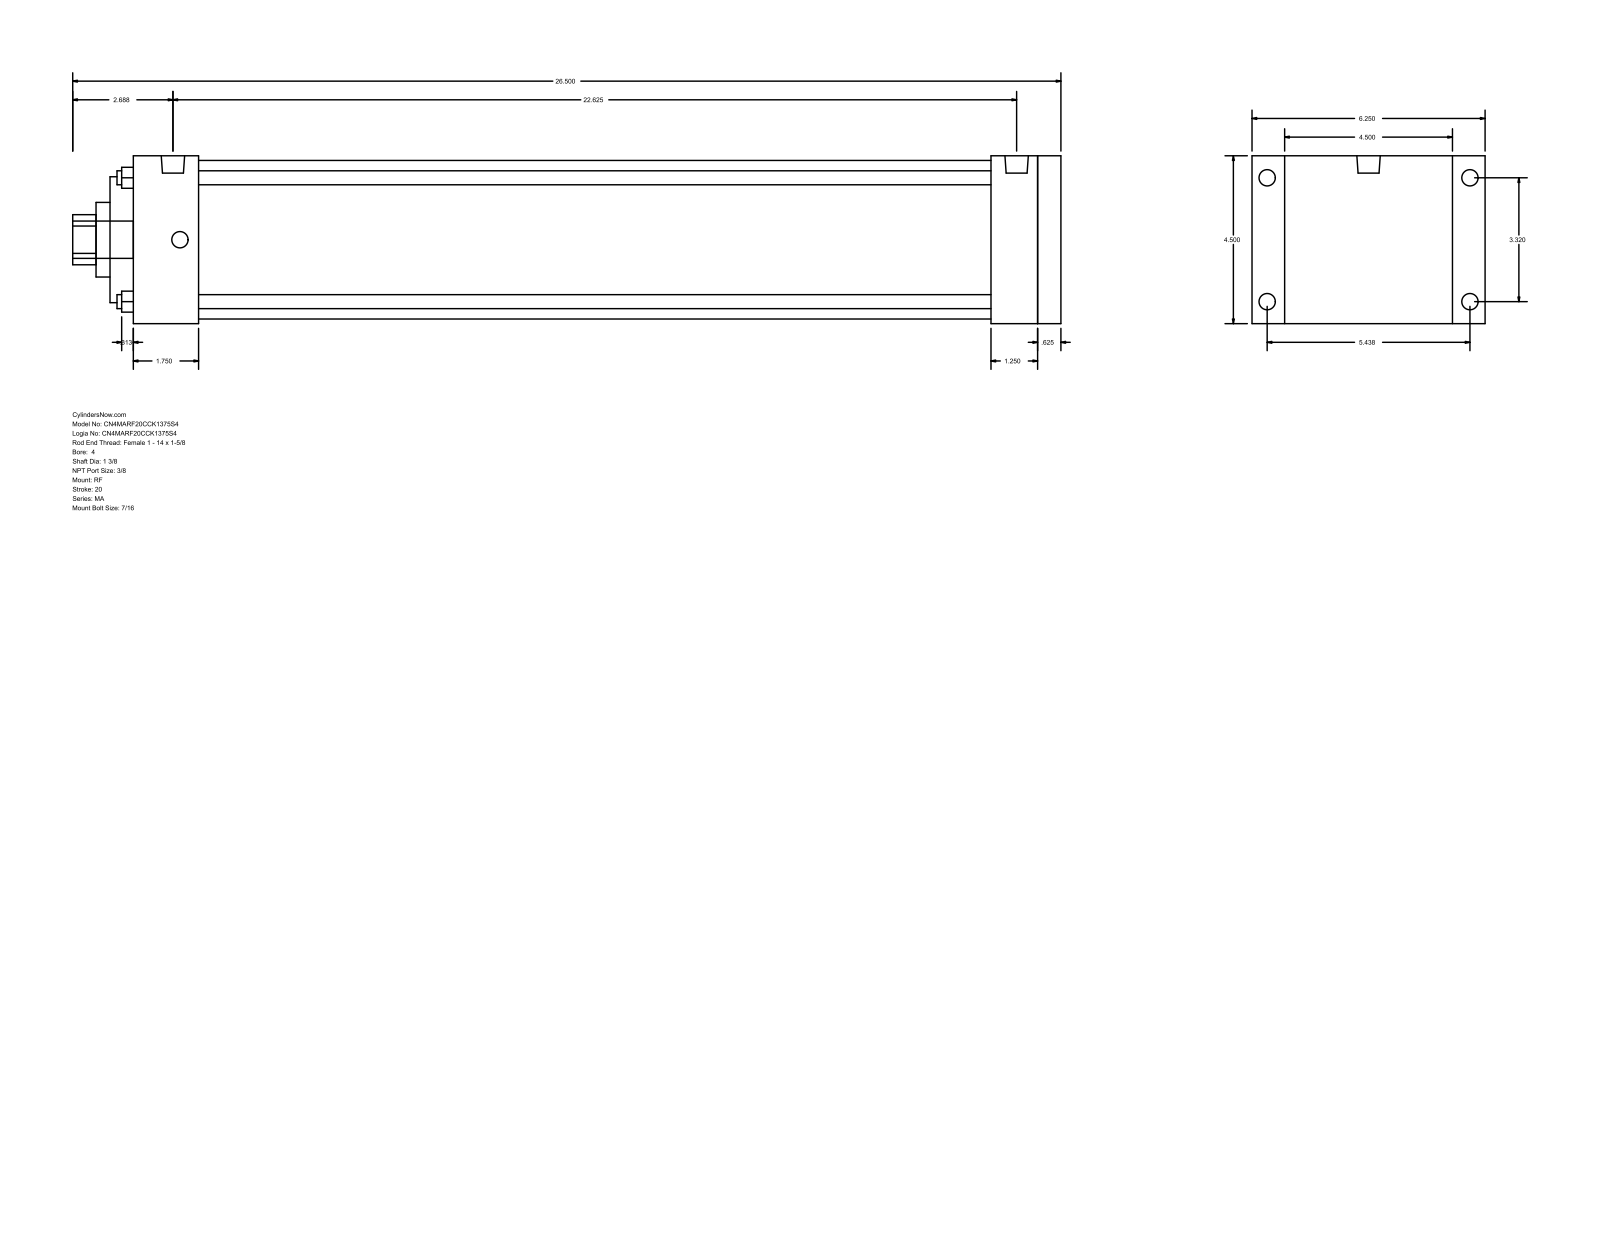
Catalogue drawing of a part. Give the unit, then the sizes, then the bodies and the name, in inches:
Units: inches
Overall size (bounding box): 26.5 × 6.25 × 4.5
Round holes (diameter × count): ⌀0.375 ×4, ⌀1.375 ×1, ⌀2 ×1, ⌀3.375 ×1, ⌀4.25 ×1
Round bosses / shafts (diameter × count): ⌀0.437 ×8, ⌀0.627 ×2, ⌀1 ×1
Partial cylindrical surfaces — rounded edges, fillets, slot ends (radius × count): R0.672 ×1
Main face-to-face distances: 4.5, 24.875, 0.625, 24.25, 25.5, 0.875, 5.375, 23.625, 23, 1.25
Hole centre spacings: 2.347, 3.32, 4.695
Bodies: 0 solids, 94 faces (65 planar, 29 cylindrical, 0 other)
Part name (STEP PRODUCT): MA_RF__0400_1.375
STEP written by: GSSL Pune (CONFIG_CONTROL_DESIGN)
